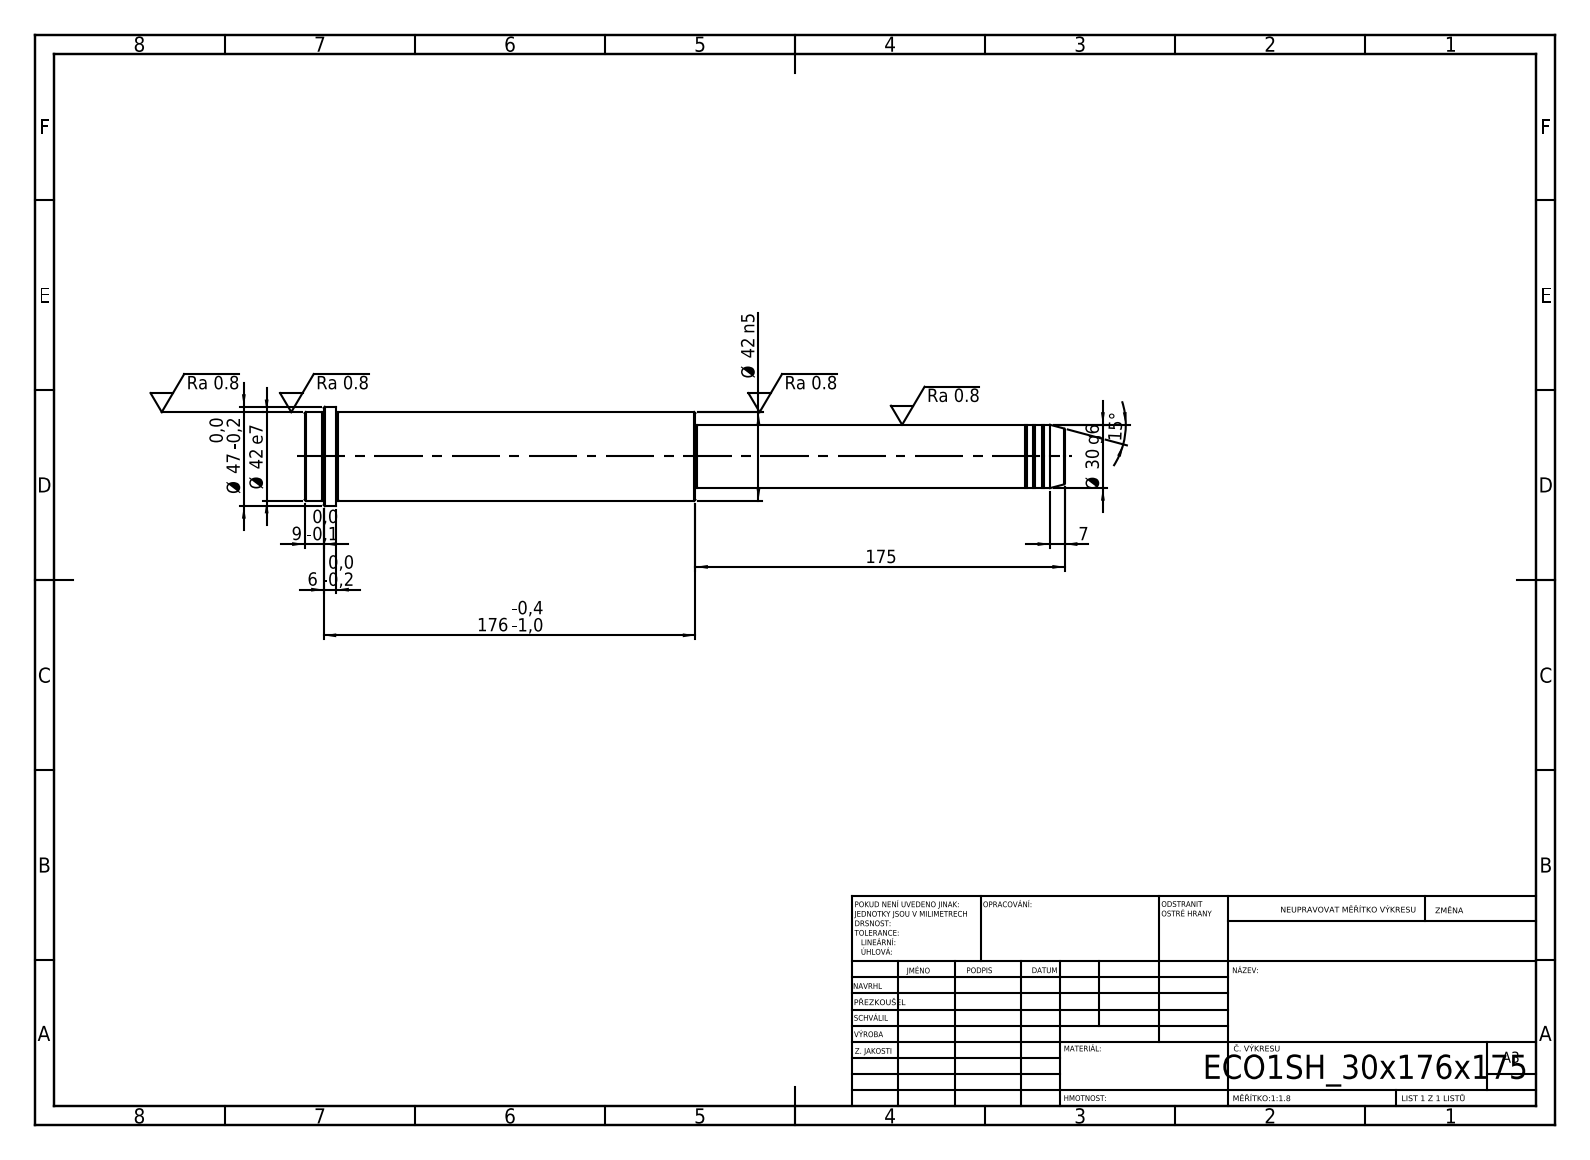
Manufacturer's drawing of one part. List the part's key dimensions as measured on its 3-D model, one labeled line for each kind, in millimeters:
STEP written by: SolidWorks 2019 (CONFIG_CONTROL_DESIGN)
Units: millimetres
Bodies: 1 solid, 52 faces (6 planar, 16 cylindrical, 30 other)
Overall size (bounding box): 360 × 47 × 47
Volume: 381 199 mm³ · Surface area: 44 537 mm²
Round bosses / shafts (diameter × count): ⌀47 ×1, ⌀42 ×1, ⌀30 ×1, ⌀29 ×1
Main face-to-face distances: 185, 175, 360, 345, 170, 15, 351, 176, 6, 9
